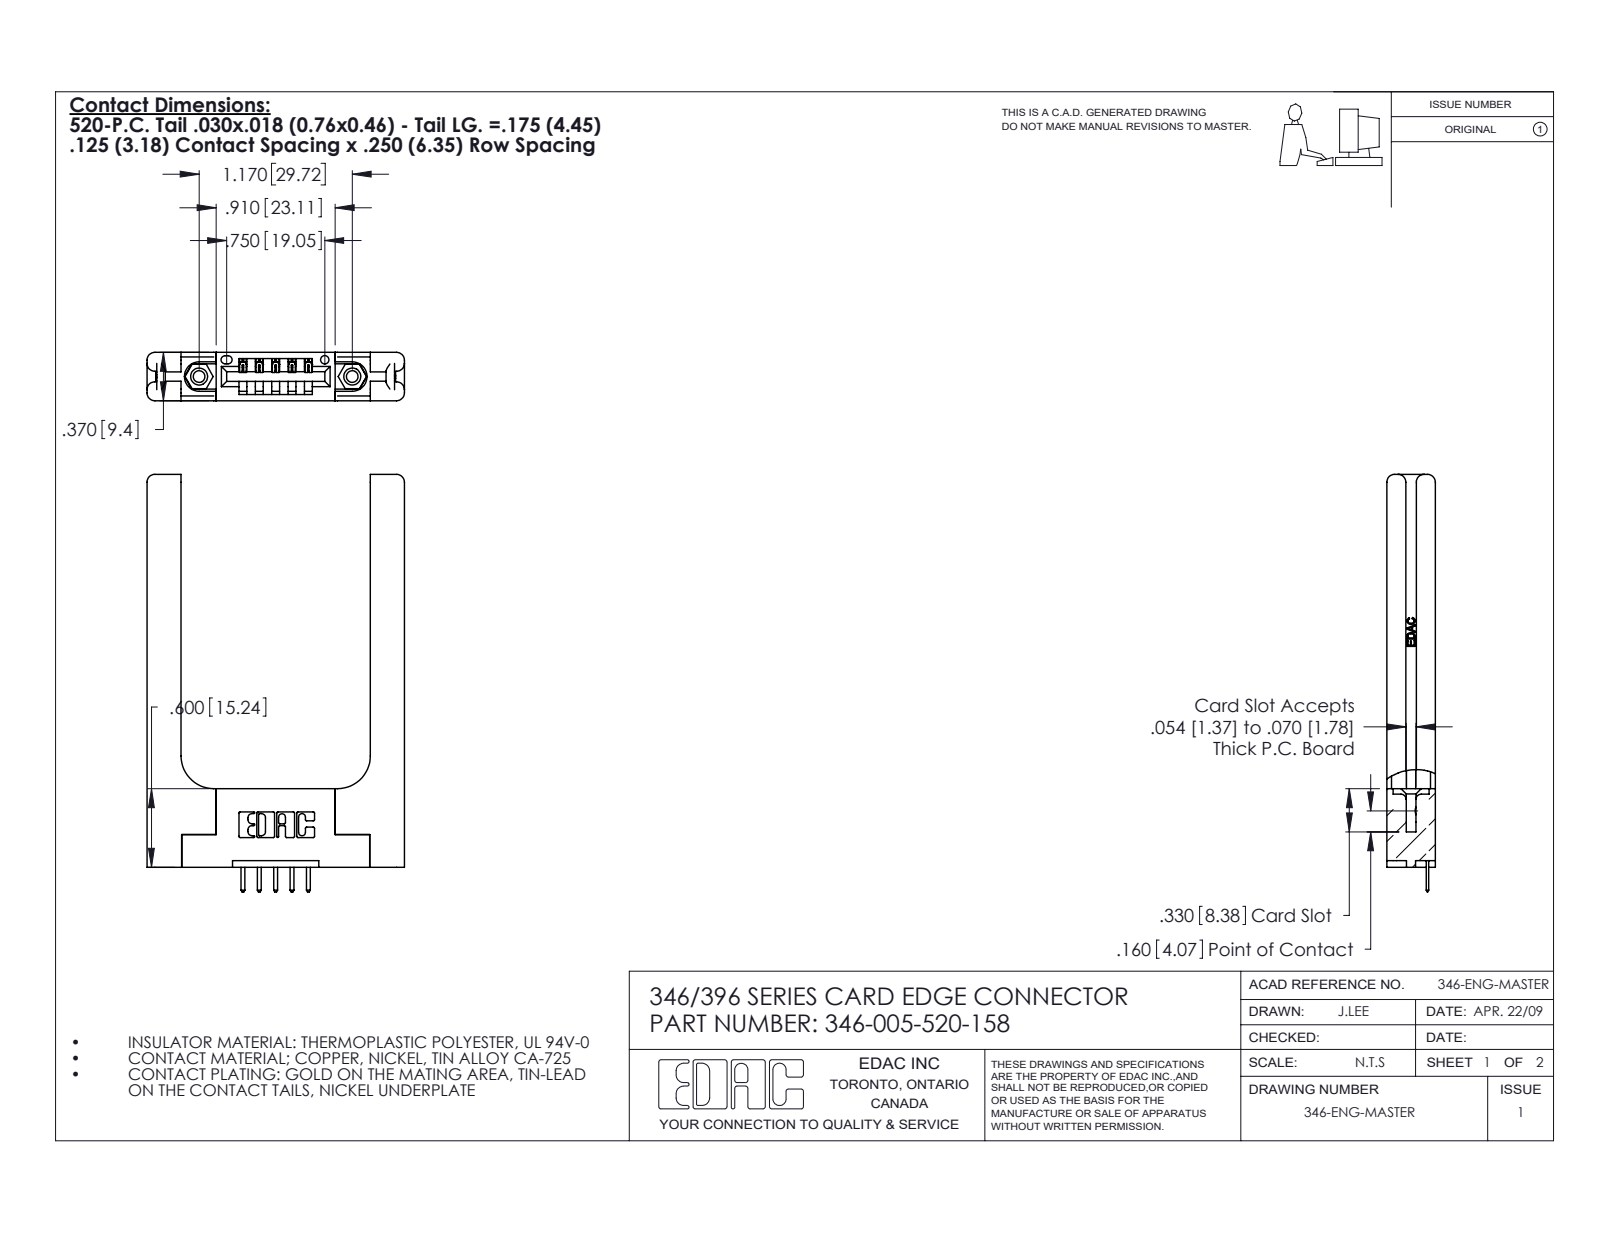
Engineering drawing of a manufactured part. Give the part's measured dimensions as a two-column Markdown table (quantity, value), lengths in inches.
| quantity | value |
| --- | --- |
| part name | 346-005-520-158; 345-250-001_345-250-001-102; 346-220-058_345-220-058; 346 Part_Flush Mounting Lugs - 0.156 Dia-TH (+1 more) |
| STEP written by | SolidWorks 2020 (CONFIG_CONTROL_DESIGN) |
| units | inches |
| bodies | 10 solids, 702 faces (448 planar, 194 cylindrical, 60 other) |
| overall size | 3.188 × 1.966 × 0.37 |
| volume | 0.733 in³ |
| surface area | 16.07 in² |
| round holes (diameter × count) | 0.089 × 2, 0.125 × 2, 0.156 × 2, 0.064 × 1 |
| round bosses / shafts (diameter × count) | 0.155 × 2 |
| partial cylindrical surfaces (radius × count) | 0.01 × 22, 0.06 × 16, 0.01 × 12, 0.006 × 10, 0.007 × 6, 0.031 × 6, 0.026 × 3, 0.03 × 2 |
| main face-to-face distances | 0.37, 0.15, 0.22, 0.25, 1.446, 0.072, 0.148, 0.071, 0.26, 1.706 |
| hole center spacings | 0.246, 0.969, 1.17 |
